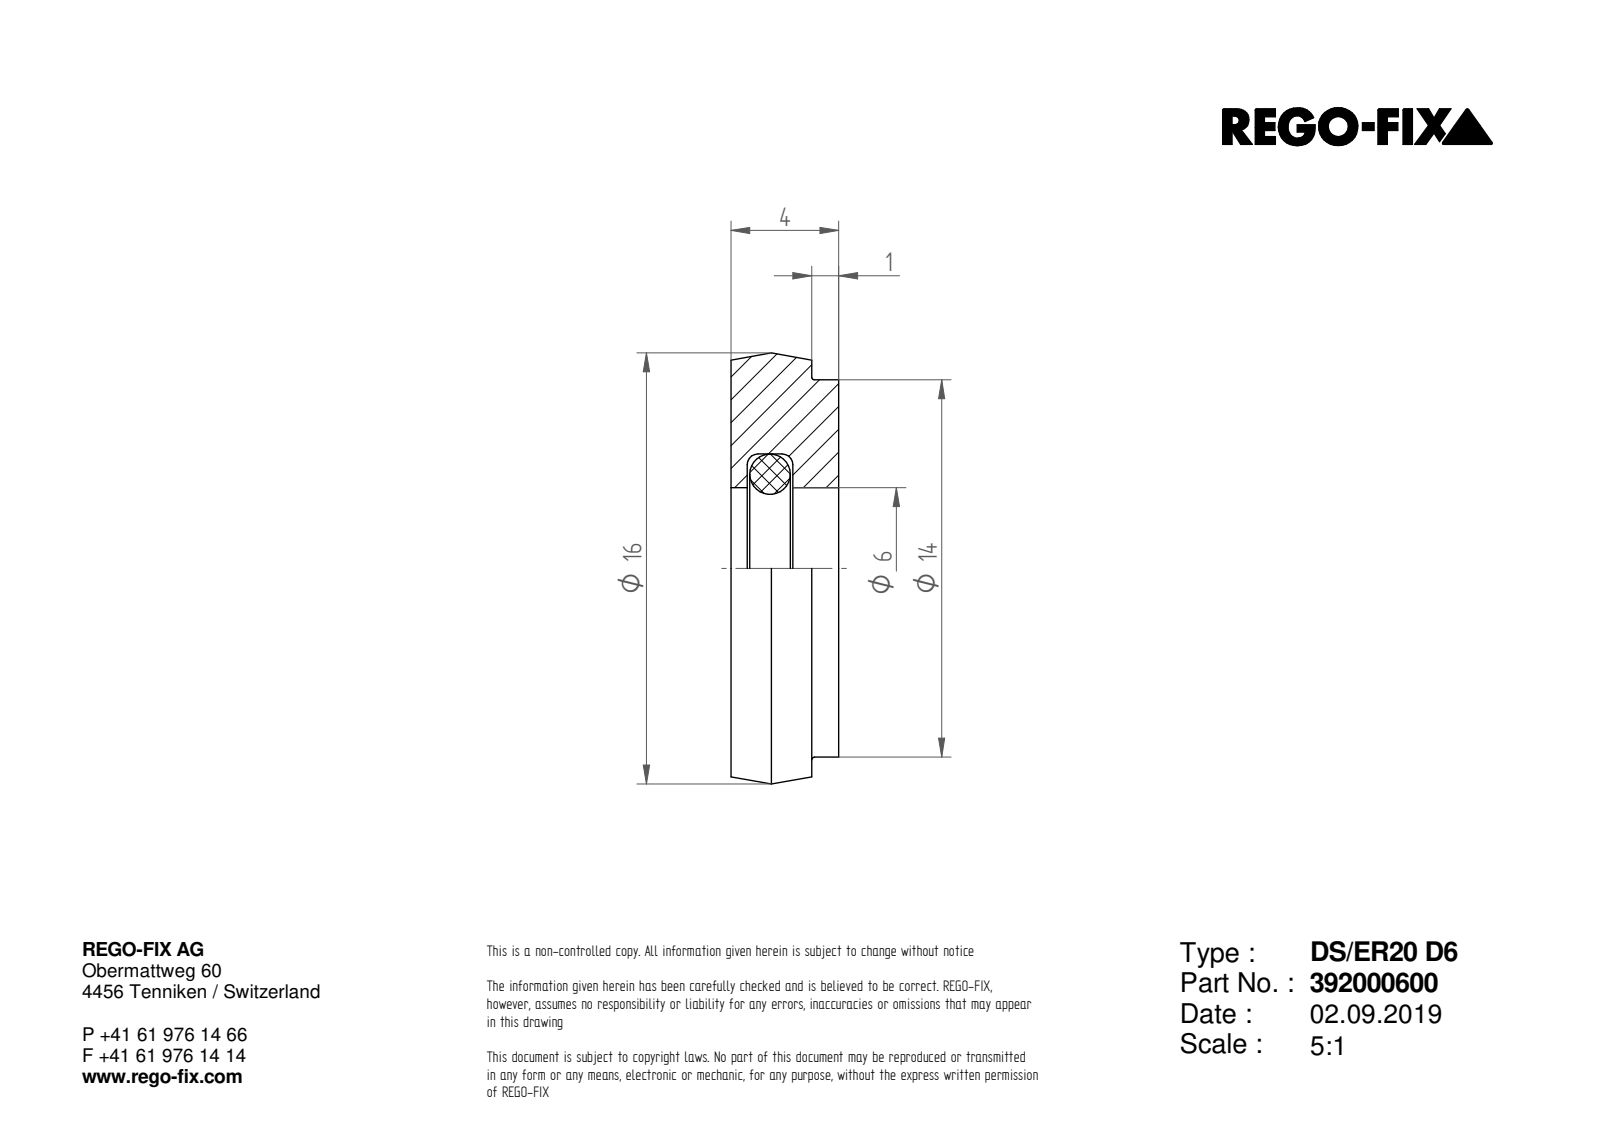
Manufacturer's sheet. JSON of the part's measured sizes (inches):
{"part_name": "NOCUT", "step_written_by": "SIEMENS PLM Software Solid Edge ST10 (AUTOMOTIVE_DESIGN)", "units": "inches", "bodies": {"solids": 1, "faces": 7, "planar": 3, "cylindrical": 3, "other": 1}, "overall_size": [0.63, 0.63, 0.157], "volume_in3": 0.039, "surface_area_in2": 0.952, "round_holes": [[0.236, 1]], "round_bosses_or_shafts": [[0.63, 1], [0.551, 1]], "face_to_face_distances": [0.157, 0.039, 0.118]}
